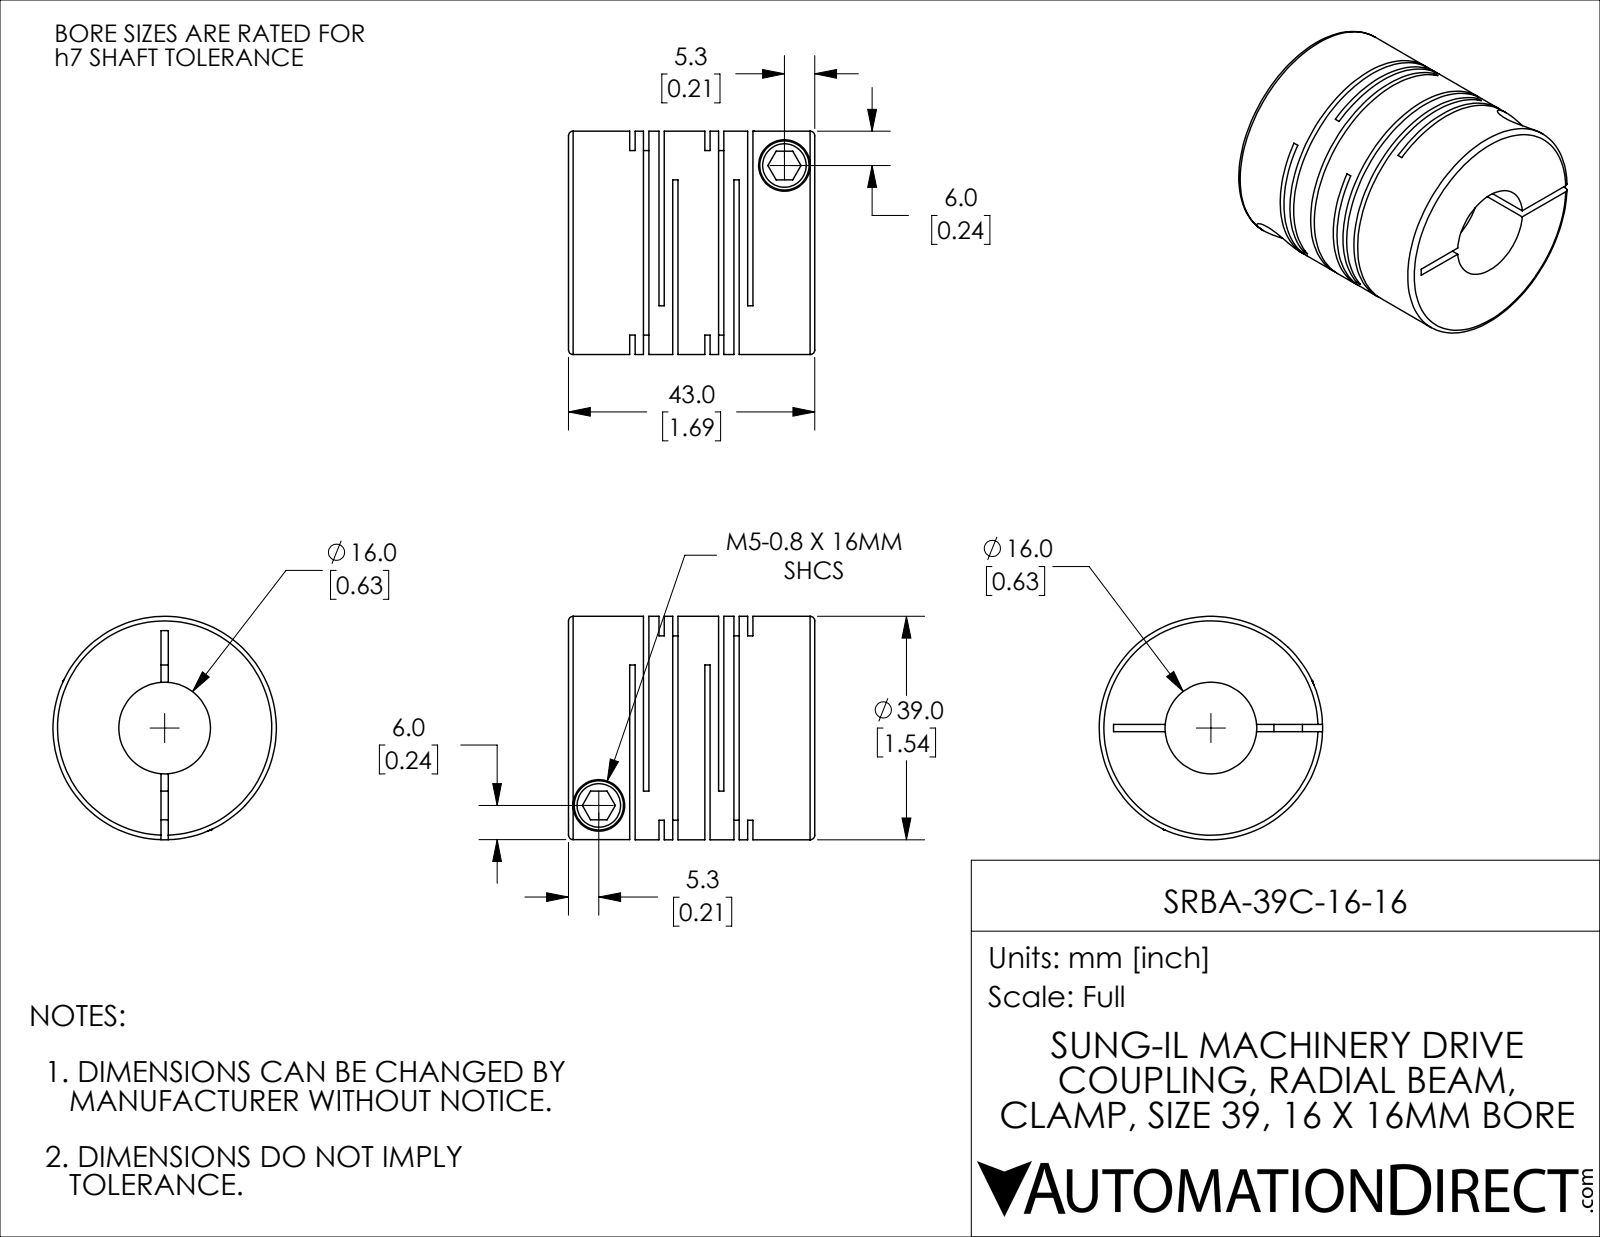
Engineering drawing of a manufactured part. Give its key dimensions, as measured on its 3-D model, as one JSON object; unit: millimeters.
{"part_name": "SRBA-39C-16-16", "step_written_by": "SolidWorks 2021 (CONFIG_CONTROL_DESIGN)", "units": "millimeters", "bodies": {"solids": 1, "faces": 114, "planar": 60, "cylindrical": 42, "other": 12}, "overall_size": [43, 39, 39], "volume_mm3": 35343, "surface_area_mm2": 22944, "round_holes": [[5, 2], [9, 2], [16, 1]], "round_bosses_or_shafts": [[8.6, 2], [39, 1]], "face_to_face_distances": [13.1, 0.92, 2.4, 5.1, 10.7, 14.02, 18.2, 1.48, 12.18, 4.18]}
